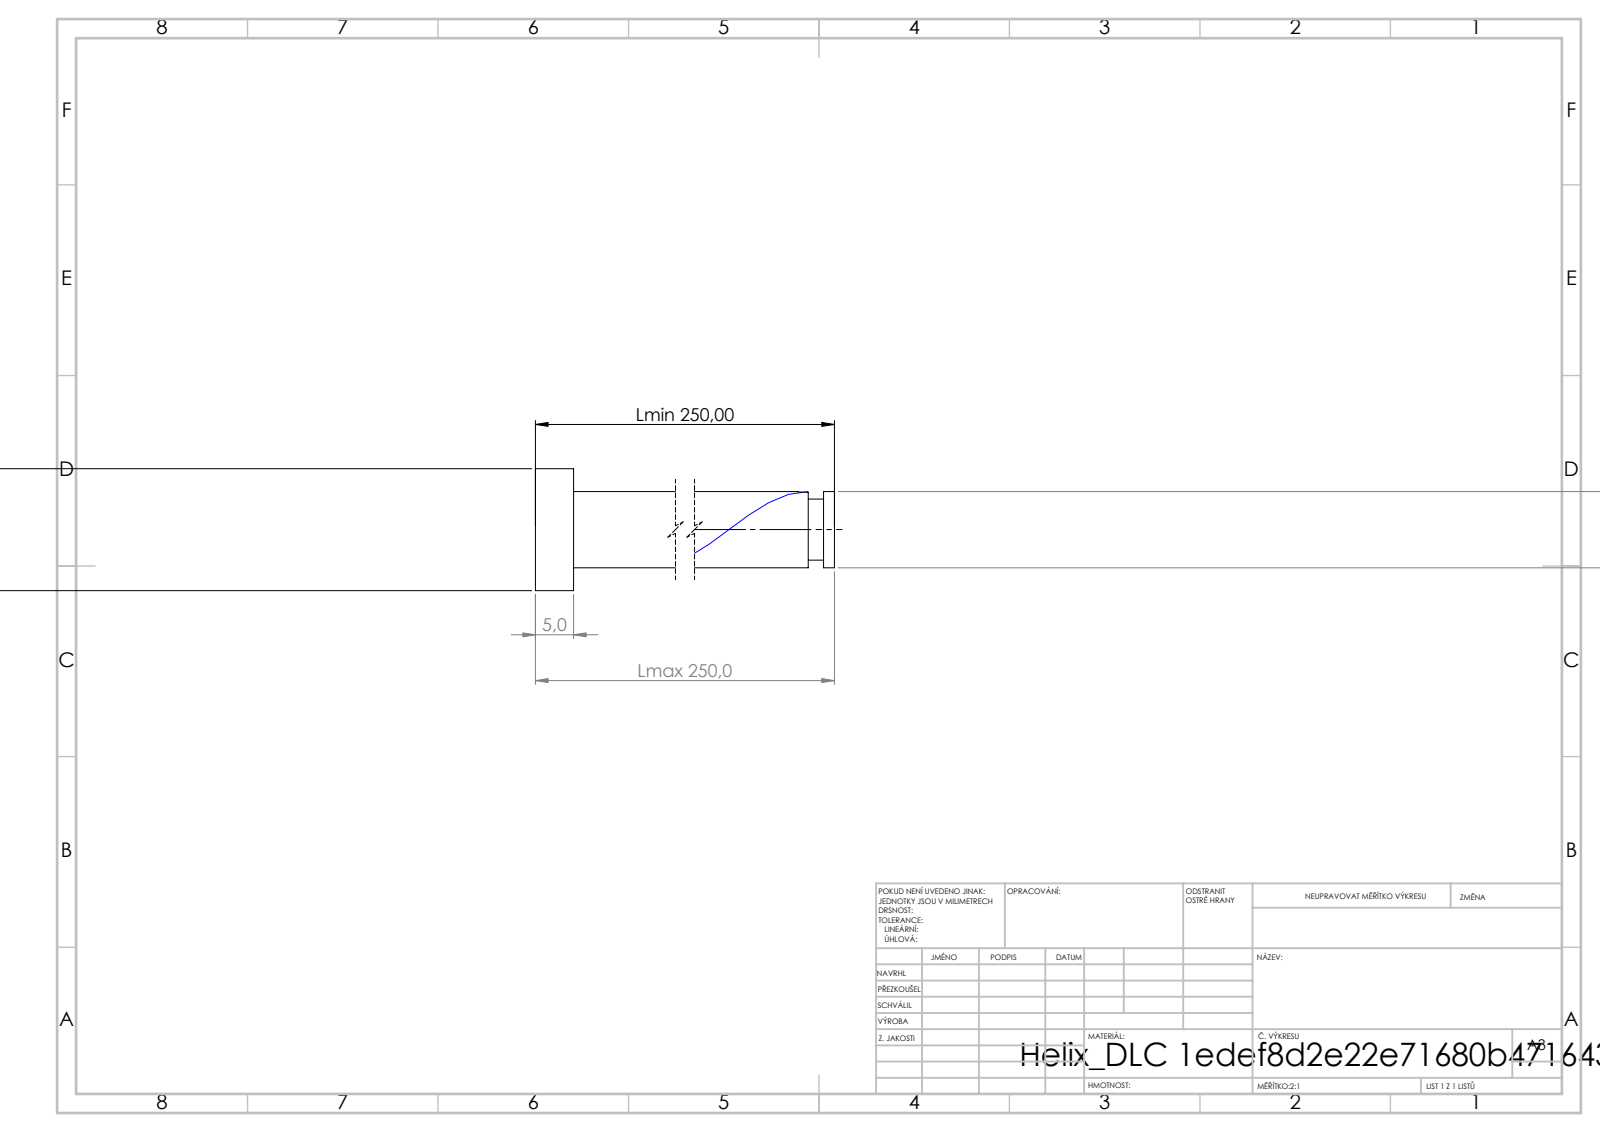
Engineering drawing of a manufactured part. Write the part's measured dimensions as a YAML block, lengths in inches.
step_written_by: "SolidWorks 2019 (CONFIG_CONTROL_DESIGN)"
units: inches
bodies: {solids: 1, faces: 21, planar: 6, cylindrical: 14, other: 1}
overall_size: [9.843, 0.63, 0.63]
volume: 1.221
surface_area: 13.26
round_bosses_or_shafts:
  - {diameter: 0.63, count: 1}
  - {diameter: 0.394, count: 1}
  - {diameter: 0.315, count: 1}
face_to_face_distances: [0.197, 9.843, 9.646, 9.786, 9.589, 0.056, 9.707, 9.511, 0.079, 0.135]
